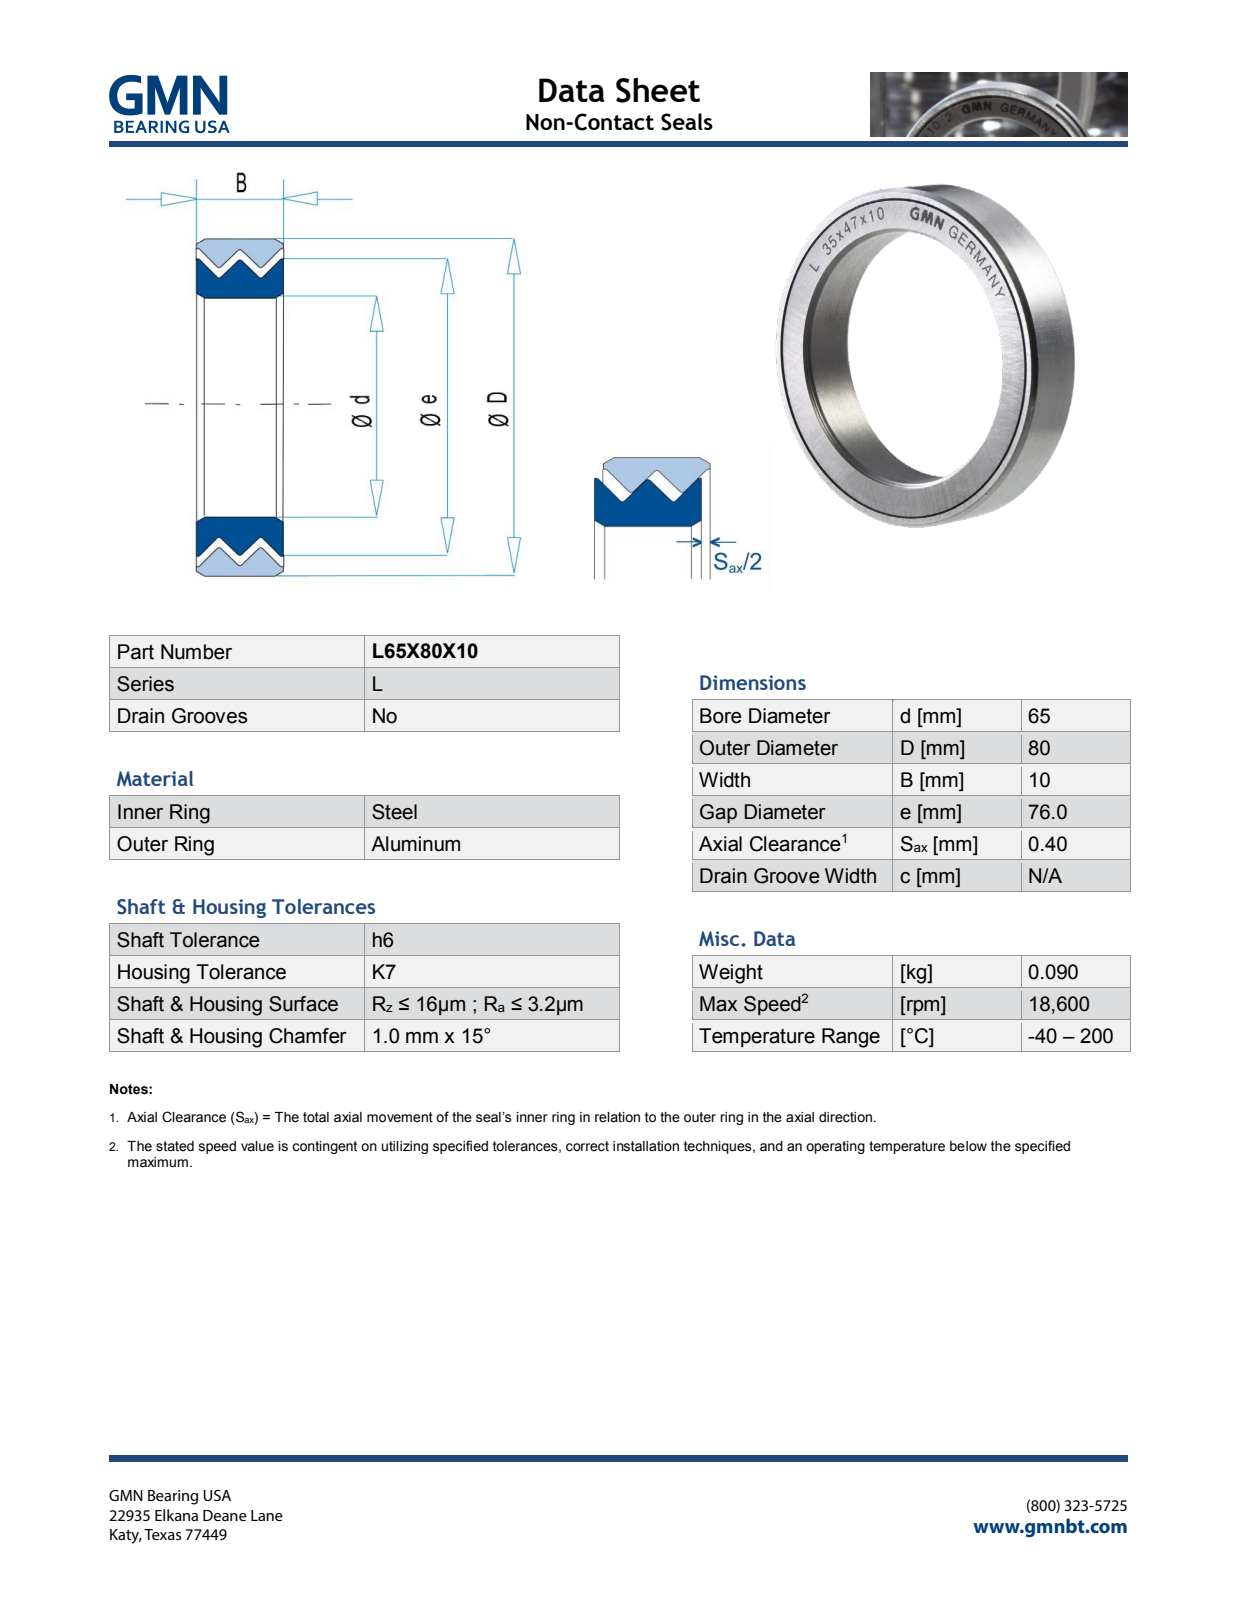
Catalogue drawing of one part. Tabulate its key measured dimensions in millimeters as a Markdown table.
| quantity | value |
| --- | --- |
| part name | L65X80X10_PRT |
| STEP written by | PRO/ENGINEER BY PARAMETRIC TECHNOLOGY CORPORATION, 2013150 (AUTOMOTIVE_DESIGN) |
| units | millimeters |
| bodies | 2 solids, 639 faces (583 planar, 12 cylindrical, 44 other) |
| overall size | 80 × 80 × 10.07 |
| volume | 16 384 mm³ |
| surface area | 13 757 mm² |
| round holes (diameter × count) | 65 × 1, 76.28 × 1 |
| round bosses / shafts (diameter × count) | 80 × 1, 76 × 1 |
| main face-to-face distances | 10, 10.07, 0.37, 0.36, 2.92, 2.56, 0.31, 2.55, 2.07, 0.33 |
